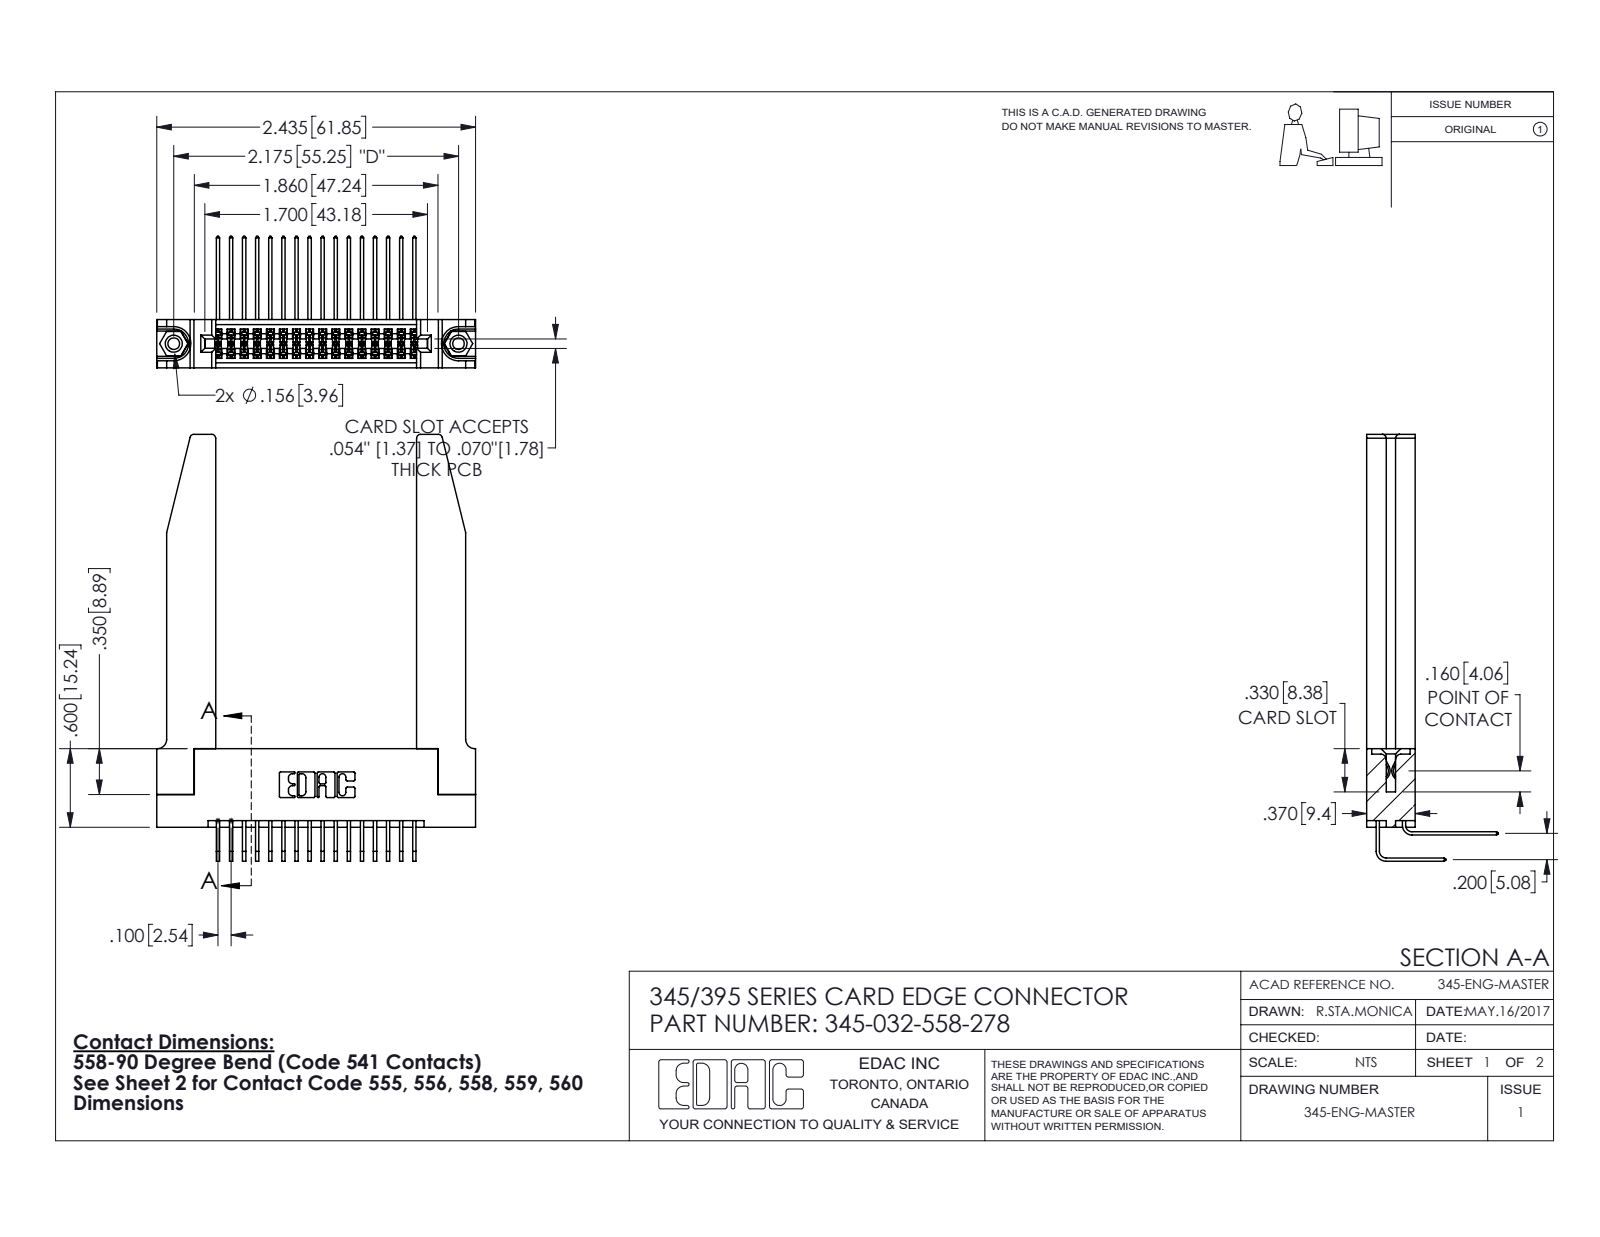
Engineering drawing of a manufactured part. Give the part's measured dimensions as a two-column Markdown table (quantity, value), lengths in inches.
| quantity | value |
| --- | --- |
| part name | 345-250-001_345-250-001-102; 345-032-558-278; 345-292-001_558 559 Tail - 1; 345-220-078_345-220-078 (+2 more) |
| STEP written by | SolidWorks 2016 (CONFIG_CONTROL_DESIGN) |
| units | inches |
| bodies | 37 solids, 2024 faces (1342 planar, 630 cylindrical, 52 other) |
| overall size | 3.259 × 2.436 × 1.005 |
| volume | 0.838 in³ |
| surface area | 24.81 in² |
| round holes (diameter × count) | 0.089 × 2, 0.125 × 2, 0.156 × 2, 0.064 × 1 |
| round bosses / shafts (diameter × count) | 0.155 × 2 |
| partial cylindrical surfaces (radius × count) | 0.006 × 64, 0.01 × 22, 0.03 × 8, 0.007 × 6, 0.031 × 6, 0.026 × 3, 0.014 × 2, 0.019 × 2 |
| main face-to-face distances | 0.37, 0.072, 0.2, 0.298, 0.148, 0.15, 0.098, 0.272, 0.025, 0.077 |
| hole center spacings | 0.27, 1.942, 2.175 |
